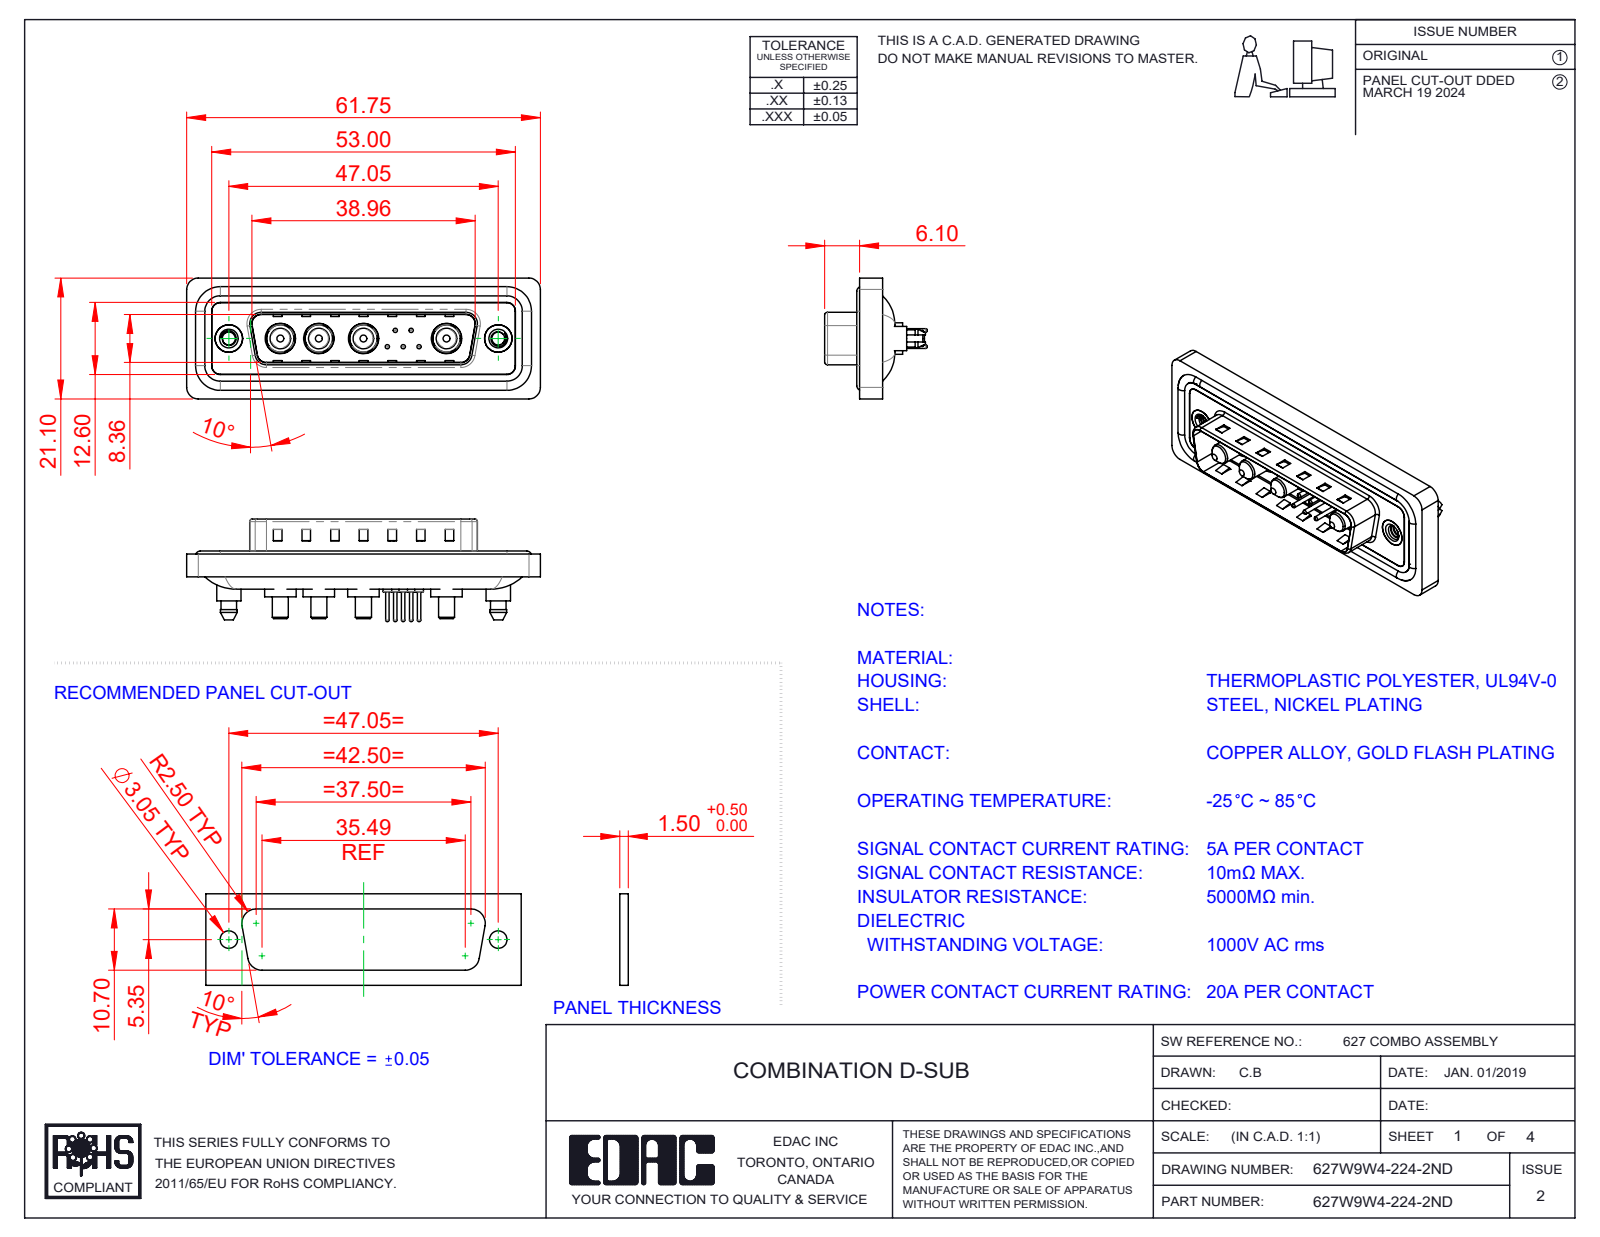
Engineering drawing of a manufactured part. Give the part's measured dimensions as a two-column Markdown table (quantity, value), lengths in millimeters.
| quantity | value |
| --- | --- |
| part name | 627W9W4-224-2ND; 627Combo Threaded Boardlock_D; 627Combo Contact Row 2_24; 627Combo Shell Rear_25 Contacts (+6 more) |
| STEP written by | SolidWorks 2023 (CONFIG_CONTROL_DESIGN) |
| units | millimeters |
| bodies | 20 solids, 882 faces (300 planar, 374 cylindrical, 208 other) |
| overall size | 61.75 × 21.1 × 17.9 |
| volume | 7 539 mm³ |
| surface area | 12 172 mm² |
| round holes (diameter × count) | 0.75 × 5, 1.6 × 5, 2 × 5, 4.85 × 4, 5.3 × 4, 2.26 × 2, 4 × 2, 4.8 × 2, 5 × 2 |
| round bosses / shafts (diameter × count) | 1.5 × 5, 0.6 × 5, 5.5 × 4, 5.2 × 4, 4.75 × 4, 3.75 × 4, 3.6 × 4, 2.8 × 4 |
| partial cylindrical surfaces (radius × count) | 1.5 × 24, 2 × 18, 1.6 × 10, 0.5 × 8, 0.25 × 4, 0.6 × 4, 0.65 × 4, 0.9 × 4 |
| main face-to-face distances | 0.4, 1.5, 1.1, 0.5, 3.1, 1.6, 2.9, 0.82, 9.58, 5.65 |
| hole center spacings | 3.16, 2.77, 5.04, 14.51, 2.78, 4.4, 4.41, 5 |
